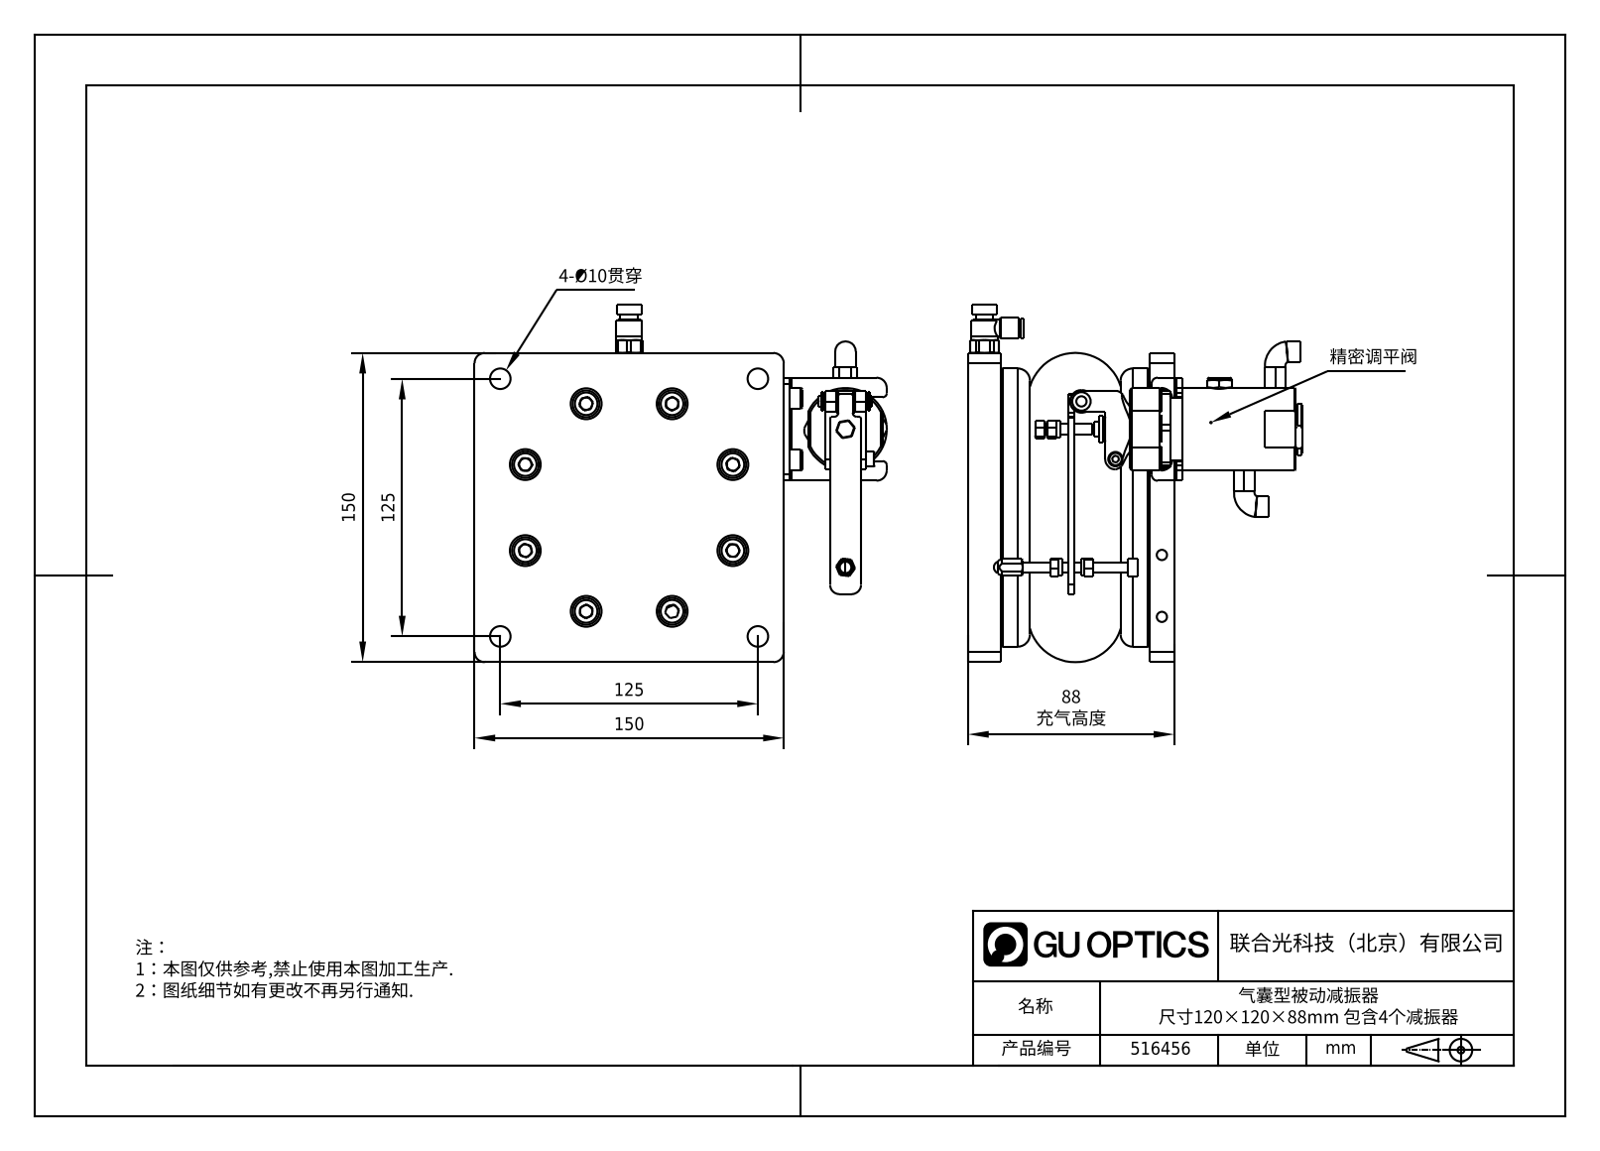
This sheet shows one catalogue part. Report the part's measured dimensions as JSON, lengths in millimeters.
{"part_name": "516456", "step_written_by": "SolidWorks 2020 (AUTOMOTIVE_DESIGN)", "units": "millimeters", "bodies": {"solids": 0, "faces": 557, "planar": 321, "cylindrical": 131, "other": 105}, "overall_size": [170, 151.13, 150], "round_holes": [[6, 1], [8, 1], [11, 1], [108, 1]], "round_bosses_or_shafts": [[5, 19], [11, 8], [10, 6], [7, 4], [8, 2], [40, 1], [30, 1], [13, 1]], "partial_cylinders_radius": [[5, 10], [0.3, 6], [2, 4], [3, 2], [4.5, 2], [0.74, 1], [4.74, 1], [7, 1]], "face_to_face_distances": [16, 76, 12, 60, 72, 88, 10, 50, 66, 120], "hole_center_spacings": [72]}
